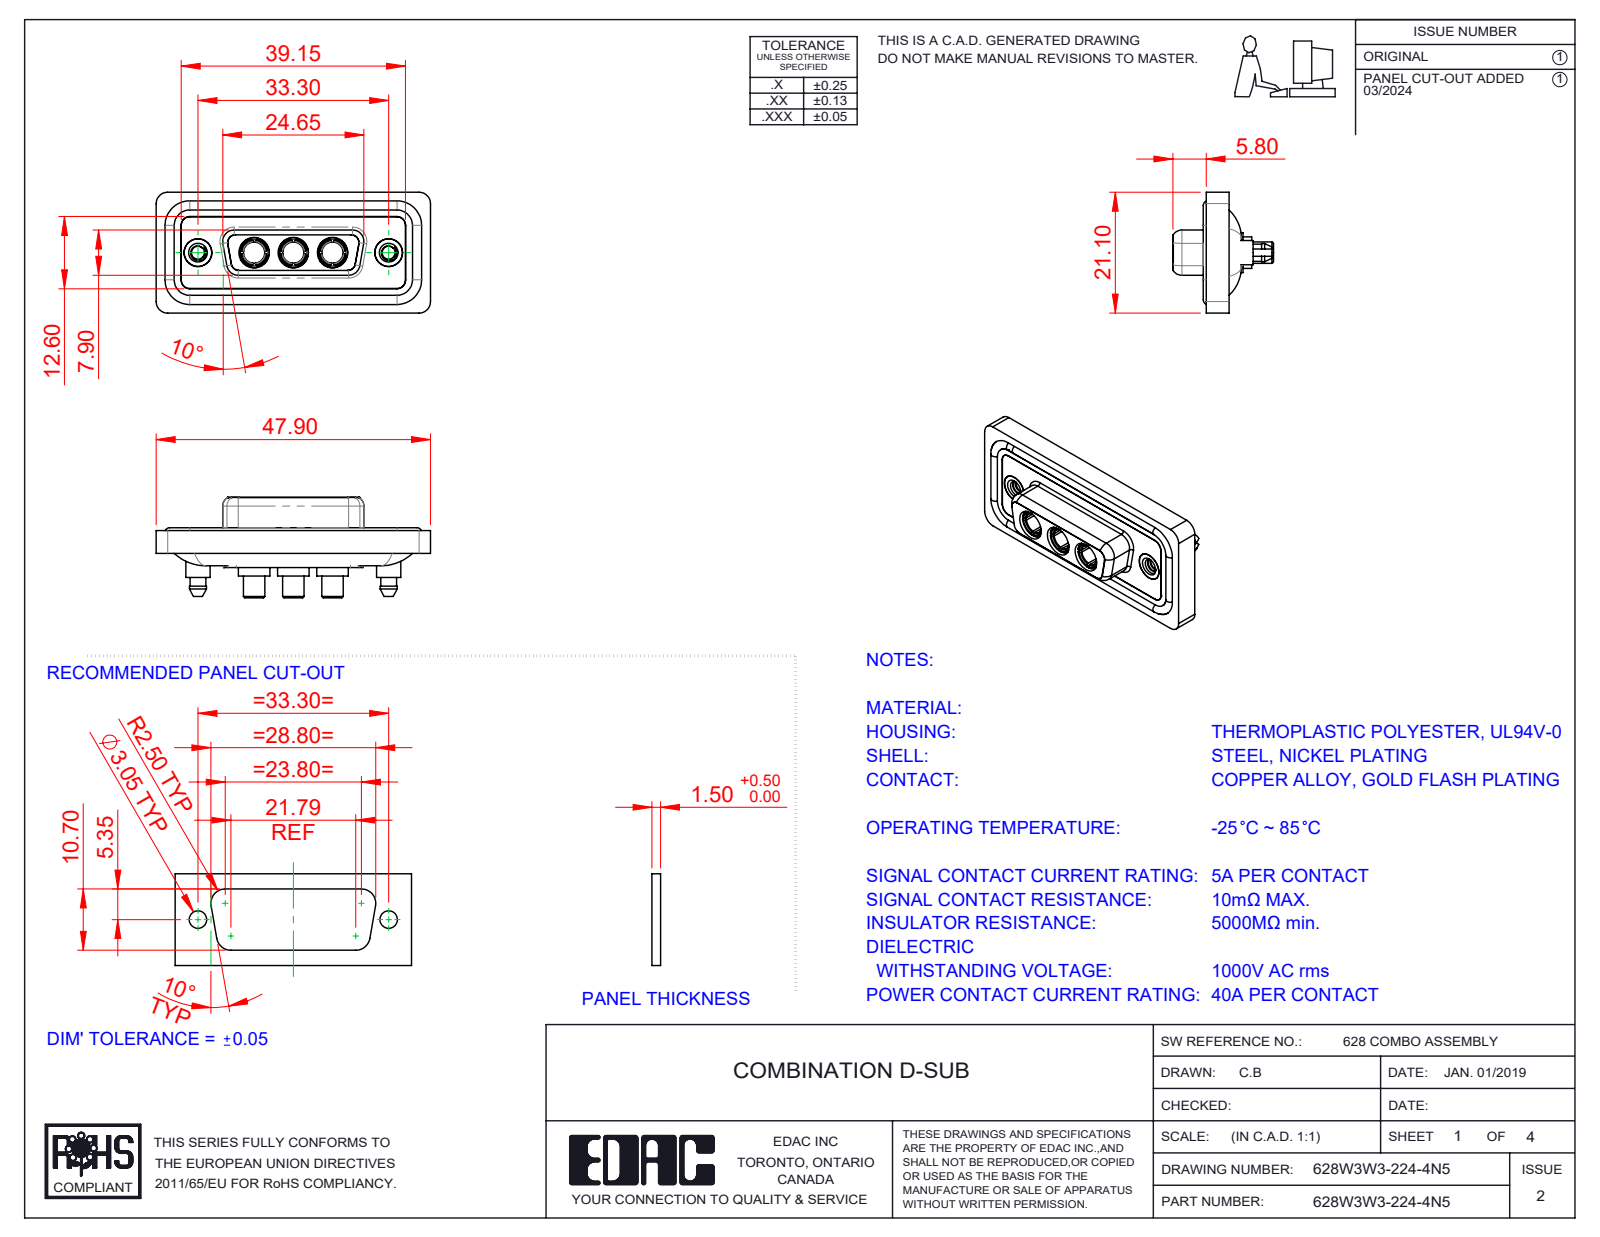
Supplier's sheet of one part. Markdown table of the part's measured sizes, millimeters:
| quantity | value |
| --- | --- |
| part name | 628Combo Shell Front_15 Contacts; 628Combo Threaded Boardlock_5; 628Combo Housing_3W3; 628W3W3-224-4N5 (+3 more) |
| STEP written by | SolidWorks 2023 (CONFIG_CONTROL_DESIGN) |
| units | millimeters |
| bodies | 13 solids, 658 faces (208 planar, 289 cylindrical, 161 other) |
| overall size | 47.9 × 21.1 × 17.55 |
| volume | 6 215 mm³ |
| surface area | 10 104 mm² |
| round holes (diameter × count) | 4.85 × 5, 3.7 × 3, 5.3 × 3, 2.26 × 2, 4 × 2, 4.05 × 2, 5 × 2 |
| round bosses / shafts (diameter × count) | 1.6 × 4, 5.5 × 3, 5.2 × 3, 4.96 × 3, 4.75 × 3, 3.75 × 3, 5.4 × 2, 4.95 × 2 |
| partial cylindrical surfaces (radius × count) | 1.5 × 24, 2 × 20, 1.35 × 12, 1.6 × 10, 0.25 × 4, 0.5 × 4, 0.6 × 4, 0.65 × 4 |
| main face-to-face distances | 0.4, 1.8, 1.6, 0.5, 7.45, 1.1, 2.9, 5.65, 7.05, 6.6 |
| hole center spacings | 6.85, 9.8, 16.65, 23.5, 13.7, 33.3 |
